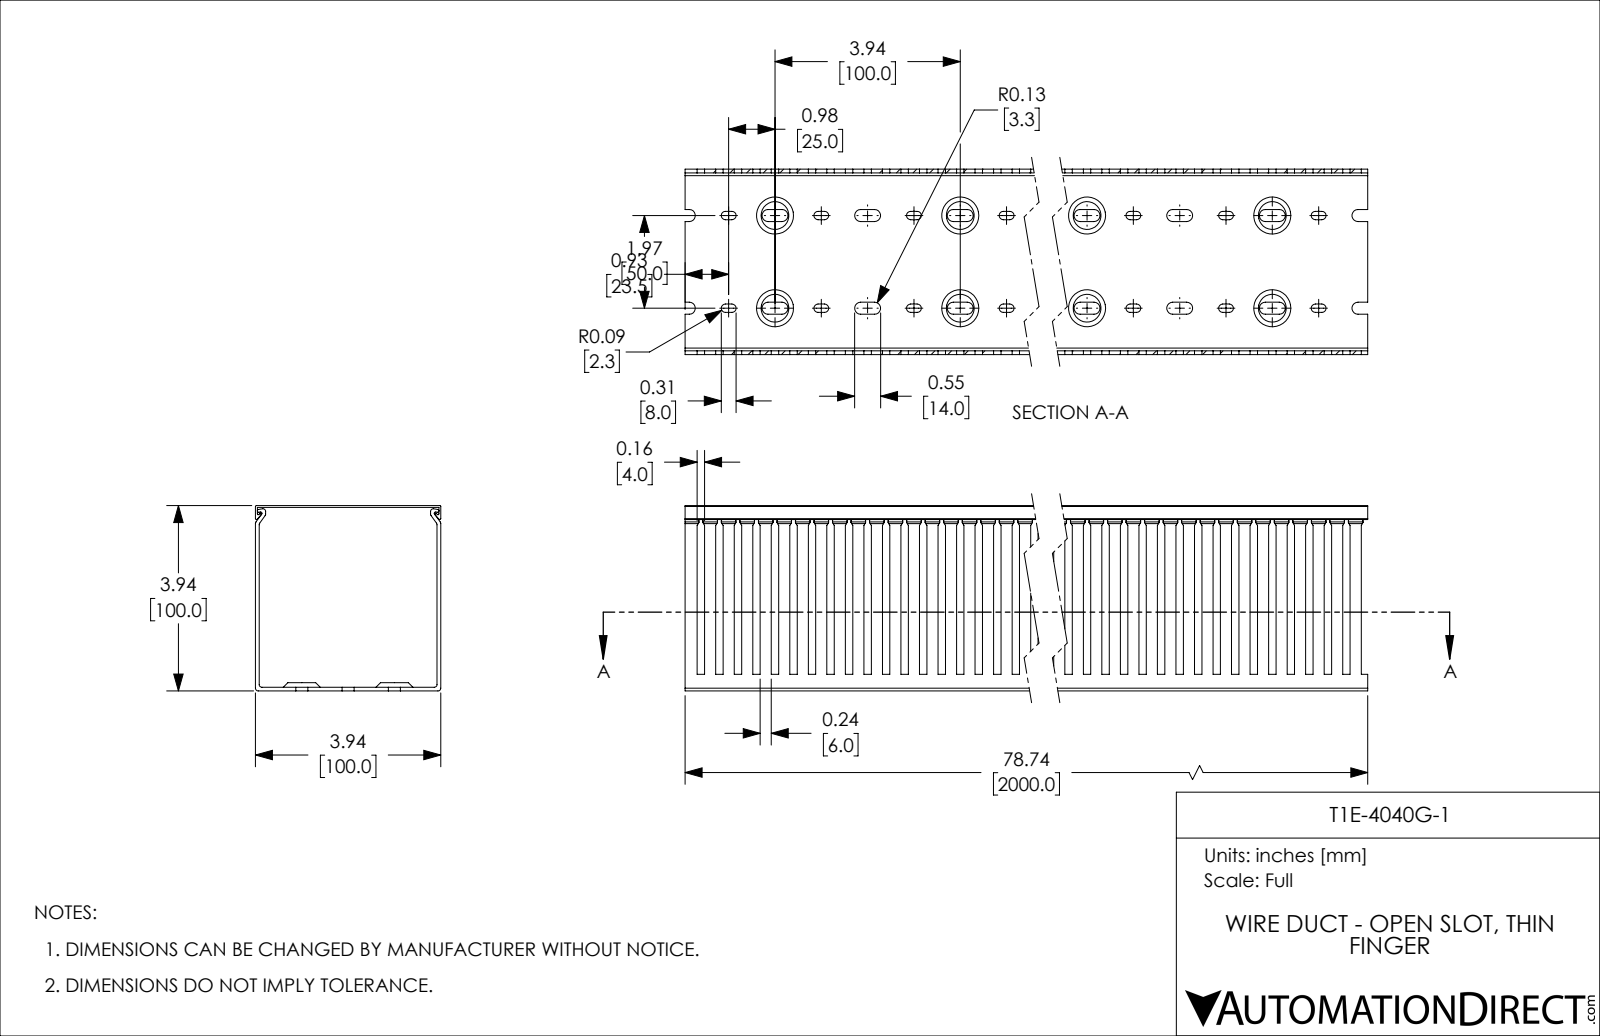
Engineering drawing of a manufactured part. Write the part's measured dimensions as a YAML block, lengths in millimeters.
part_name: "T1E-4040G-1"
step_written_by: "SolidWorks 2021 (CONFIG_CONTROL_DESIGN)"
units: millimeters
bodies: {solids: 2, faces: 1573, planar: 762, cylindrical: 731, other: 80}
overall_size: [2000, 100, 100]
volume: 1411000
surface_area: 1652000
partial_cylinders:
  - {radius: 3.25, count: 200}
  - {radius: 2.25, count: 160}
  - {radius: 1.5, count: 12}
  - {radius: 0.5, count: 8}
  - {radius: 0.75, count: 6}
face_to_face_distances: [2, 98, 100, 1, 99, 97, 96, 4.5, 94.5, 5.5]
